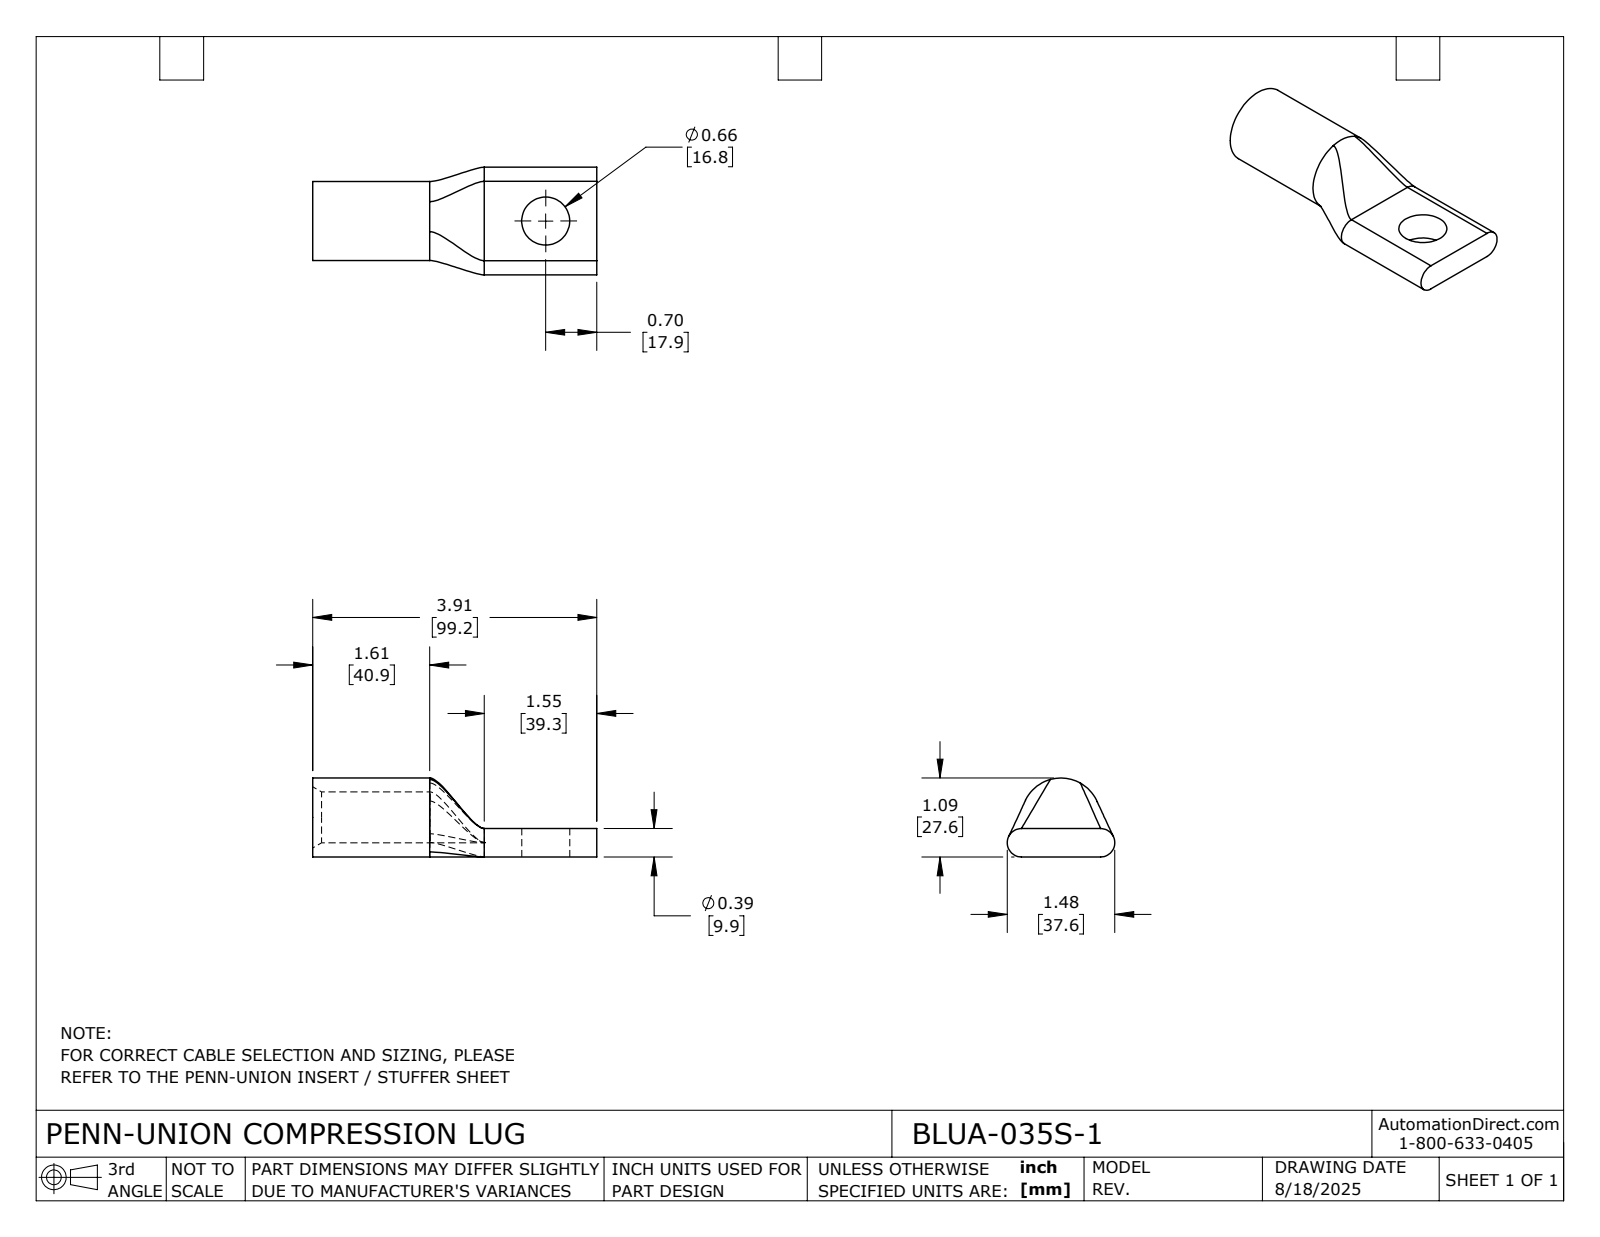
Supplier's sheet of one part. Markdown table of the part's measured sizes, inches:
| quantity | value |
| --- | --- |
| part name | BLUA-035S-1 |
| STEP written by | SolidWorks 2024 (CONFIG_CONTROL_DESIGN) |
| units | inches |
| bodies | 1 solid, 24 faces (5 planar, 9 cylindrical, 10 other) |
| overall size | 3.906 × 1.48 × 1.085 |
| volume | 1.971 in³ |
| surface area | 20.07 in² |
| round holes (diameter × count) | 0.66 × 1, 0.7 × 1 |
| round bosses / shafts (diameter × count) | 1.085 × 1 |
| partial cylindrical surfaces (radius × count) | 0.195 × 2 |
| main face-to-face distances | 0.39, 3.906, 2.359, 1.547 |
